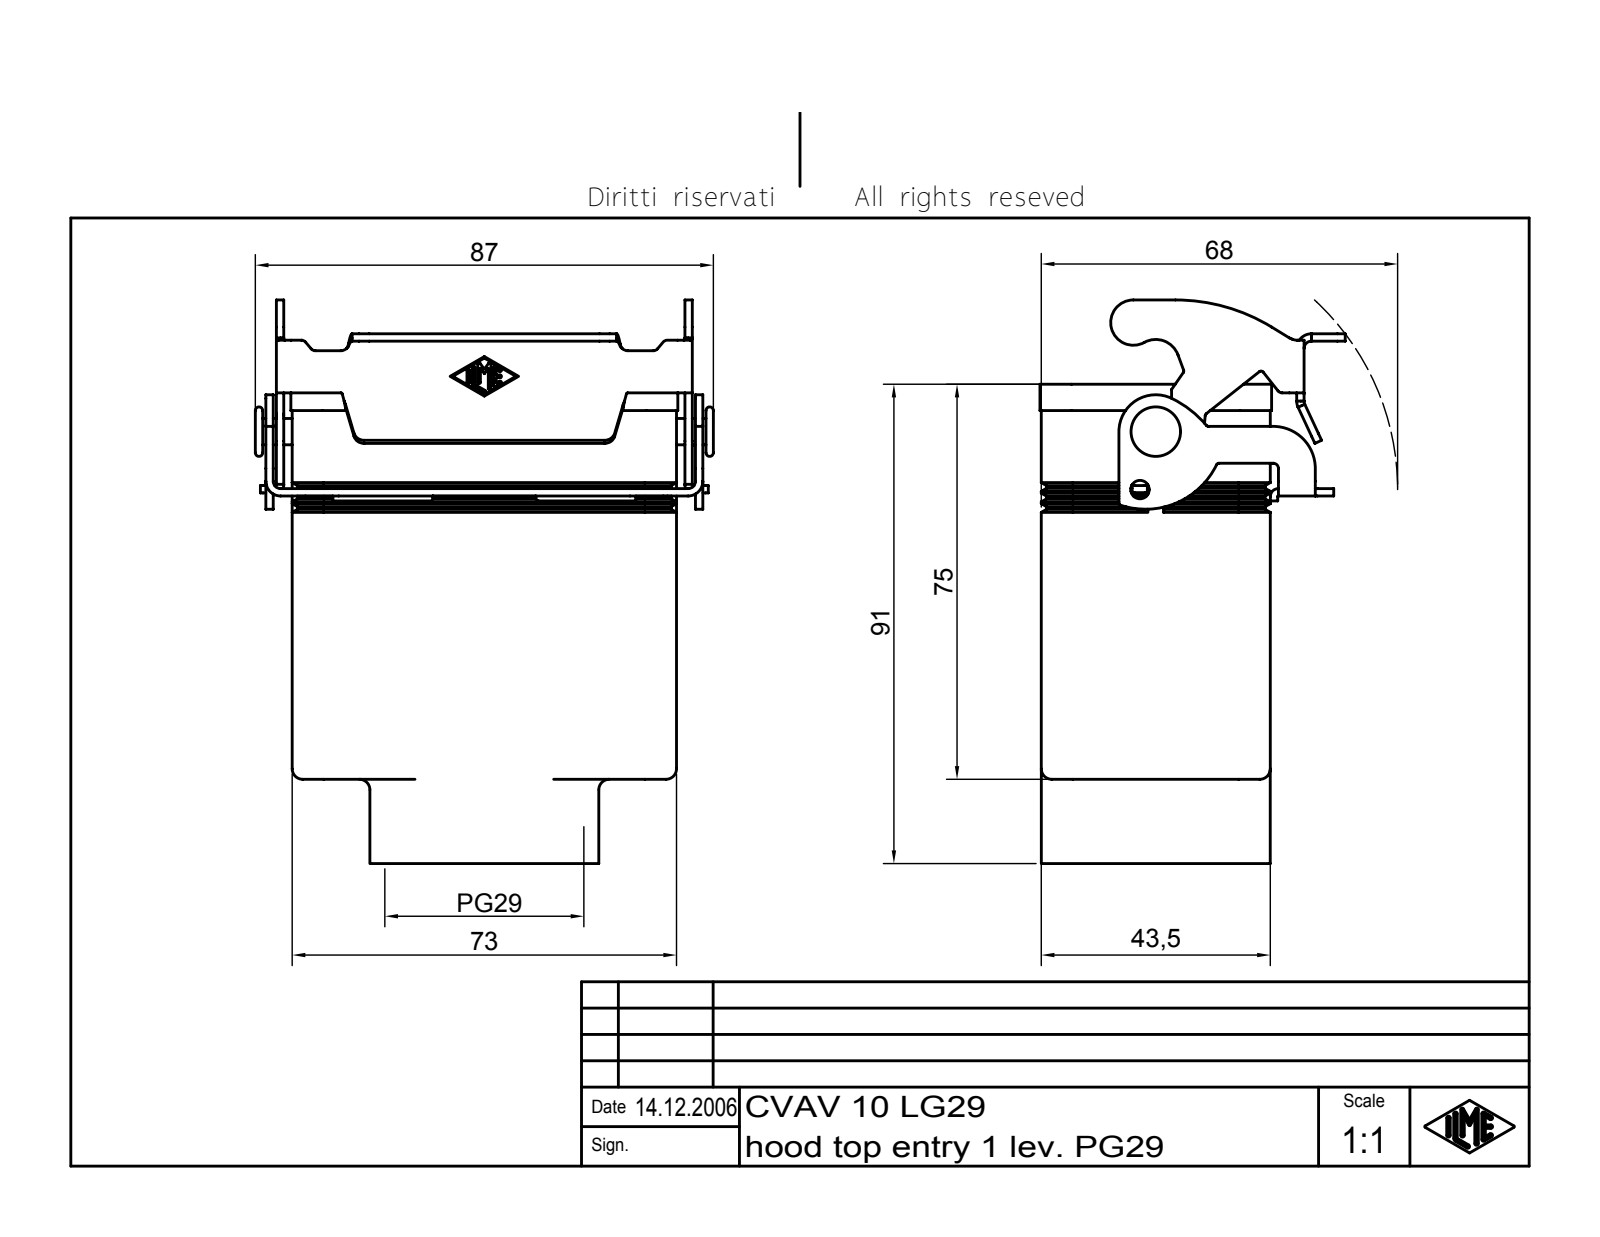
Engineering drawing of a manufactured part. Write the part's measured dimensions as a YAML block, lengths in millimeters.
part_name: "CVAV 10 LG29"
step_written_by: "Autodesk Inventor 7 (AUTOMOTIVE_DESIGN)"
units: millimeters
bodies: {solids: 2, faces: 501, planar: 156, cylindrical: 129, other: 216}
overall_size: [107, 87, 57.98]
volume: 84944
surface_area: 52501
round_holes:
  - {diameter: 3.5, count: 1}
  - {diameter: 32.48, count: 1}
  - {diameter: 35.48, count: 1}
round_bosses_or_shafts:
  - {diameter: 43.48, count: 1}
  - {diameter: 5, count: 1}
  - {diameter: 3.2, count: 1}
partial_cylinders:
  - {radius: 0.25, count: 15}
  - {radius: 2, count: 10}
  - {radius: 0.5, count: 9}
  - {radius: 1.5, count: 9}
  - {radius: 1, count: 8}
  - {radius: 6, count: 8}
  - {radius: 1.4, count: 6}
  - {radius: 2.8, count: 6}
face_to_face_distances: [3, 40.5, 43.5, 37.5, 70, 73, 11.75, 8.75, 1.4, 11.5]
